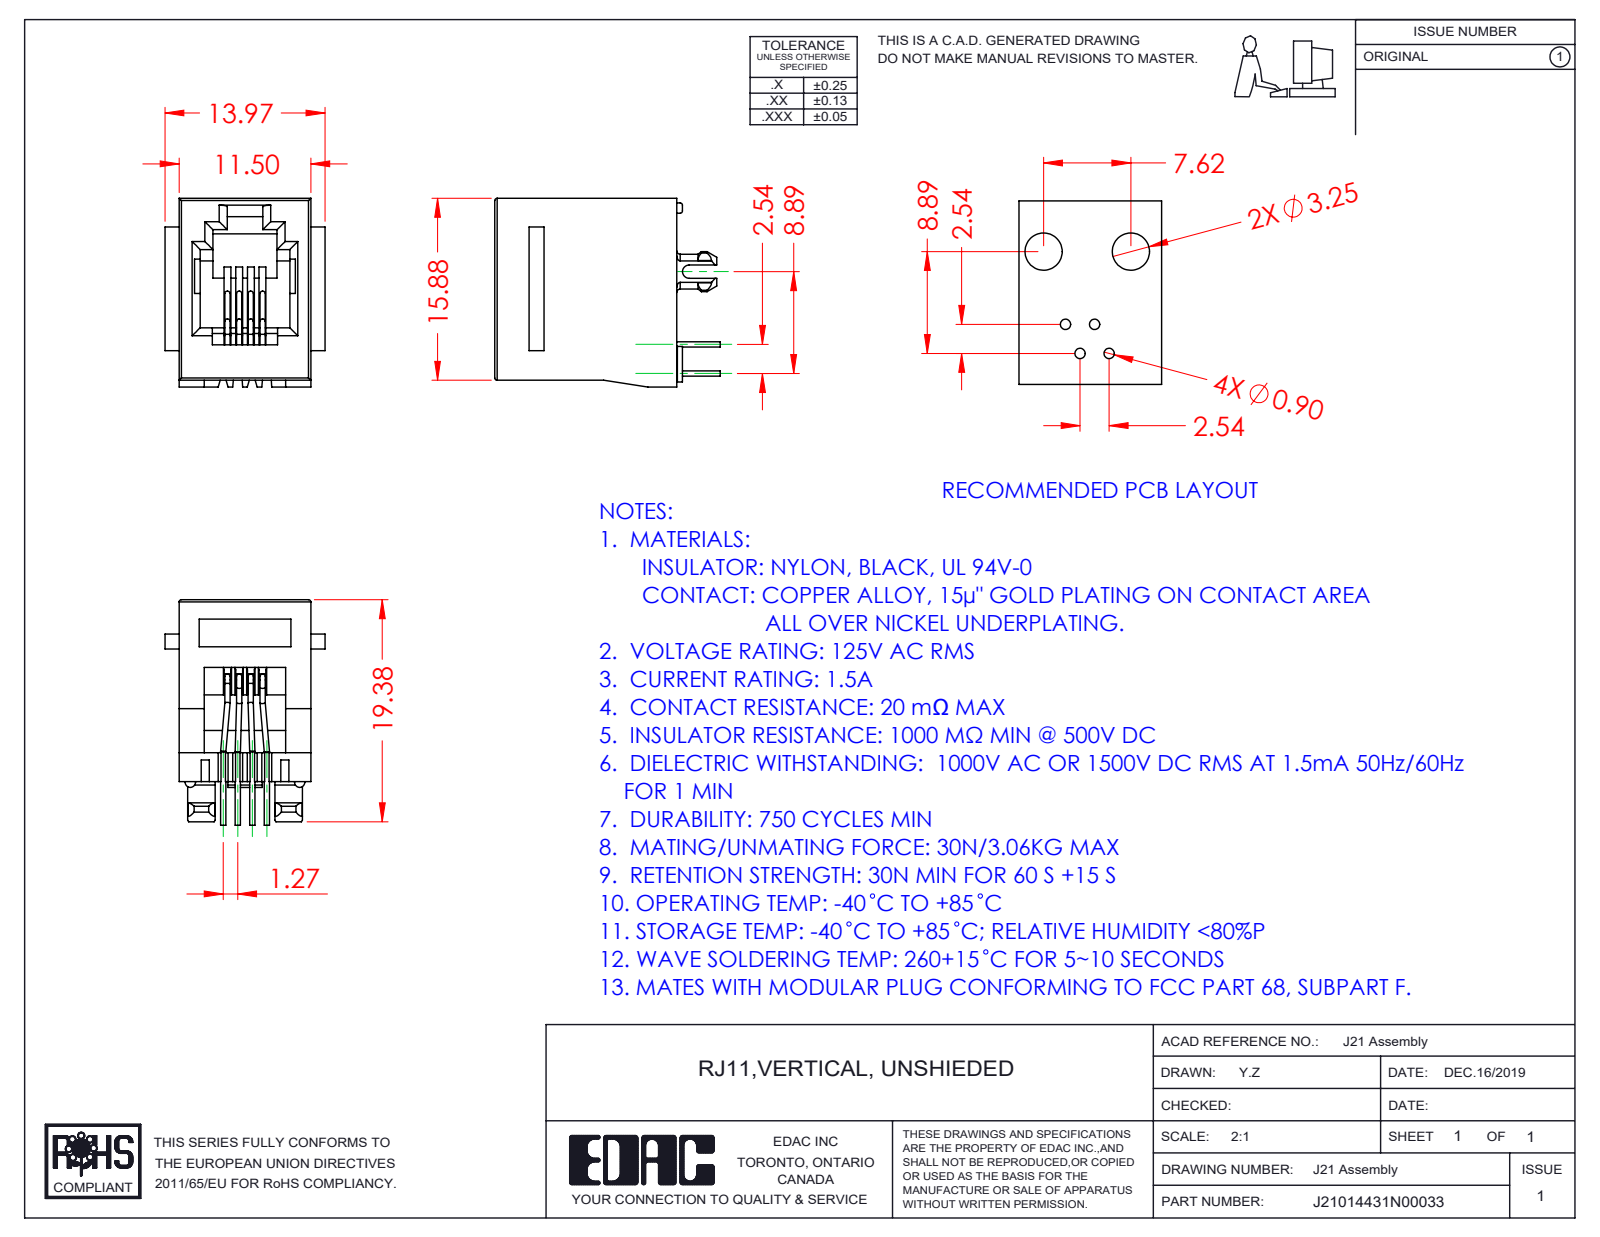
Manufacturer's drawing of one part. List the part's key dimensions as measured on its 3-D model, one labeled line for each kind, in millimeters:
Part name (STEP PRODUCT): 21 Insulator; 21 Contacts; RJ21014431N00033
STEP written by: SolidWorks 2016 (CONFIG_CONTROL_DESIGN)
Units: millimetres
Bodies: 5 solids, 369 faces (230 planar, 111 cylindrical, 28 other)
Overall size (bounding box): 19.68 × 16.48 × 13.97
Volume: 1 616 mm³ · Surface area: 2 564 mm²
Round holes (diameter × count): ⌀2 ×2
Round bosses / shafts (diameter × count): ⌀0.46 ×24
Partial cylindrical surfaces — rounded edges, fillets, slot ends (radius × count): R0.5 ×9, R0.7 ×9, R0.2 ×7, R0.23 ×4, R0.45 ×2, R1.52 ×2, R1.75 ×2, R0.57 ×1
Main face-to-face distances: 11.5, 1.6, 15.88, 1.02, 7.2, 0.6, 2.95, 8.55, 2.04, 1.35
Hole centre spacings: 8.4
